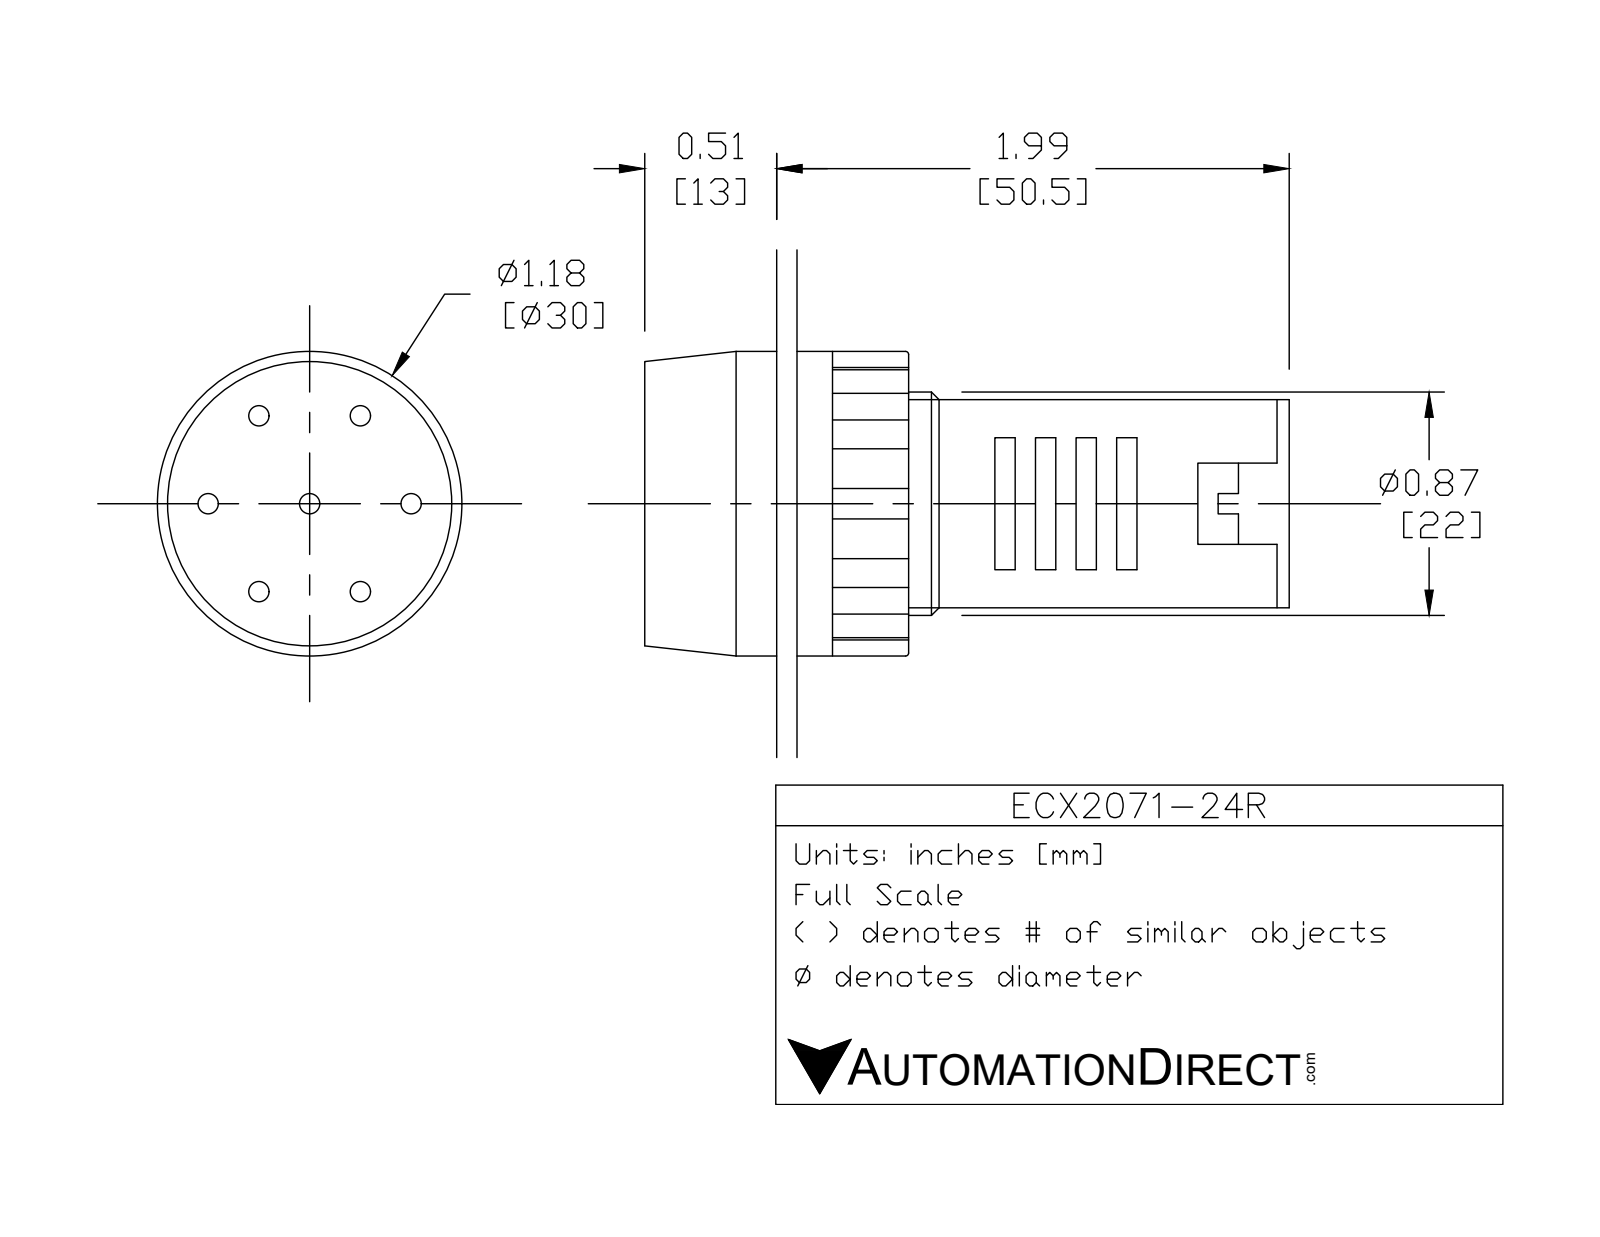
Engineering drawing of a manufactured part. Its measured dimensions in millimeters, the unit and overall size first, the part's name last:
Units: millimetres
Overall size (bounding box): 63.5 × 30 × 30
Round holes (diameter × count): ⌀2 ×4, ⌀5.5 ×2, ⌀22 ×1, ⌀22.5 ×1
Round bosses / shafts (diameter × count): ⌀4 ×2, ⌀30 ×1, ⌀29 ×1, ⌀26.5 ×1, ⌀20 ×1
Partial cylindrical surfaces — rounded edges, fillets, slot ends (radius × count): R0.25 ×22, R1 ×8, R9 ×1
Main face-to-face distances: 2, 4, 6, 8, 10, 12, 12.5, 16, 0.5, 13
Hole centre spacings: 7.48, 10, 13.66, 14.14, 4.62, 20, 9.24
Volume: 26 255 mm³ · Surface area: 12 389 mm²
Bodies: 6 solids, 196 faces (89 planar, 79 cylindrical, 28 other)
Part name (STEP PRODUCT): ECX2071-24
STEP written by: SolidWorks 2017 (AUTOMOTIVE_DESIGN)
